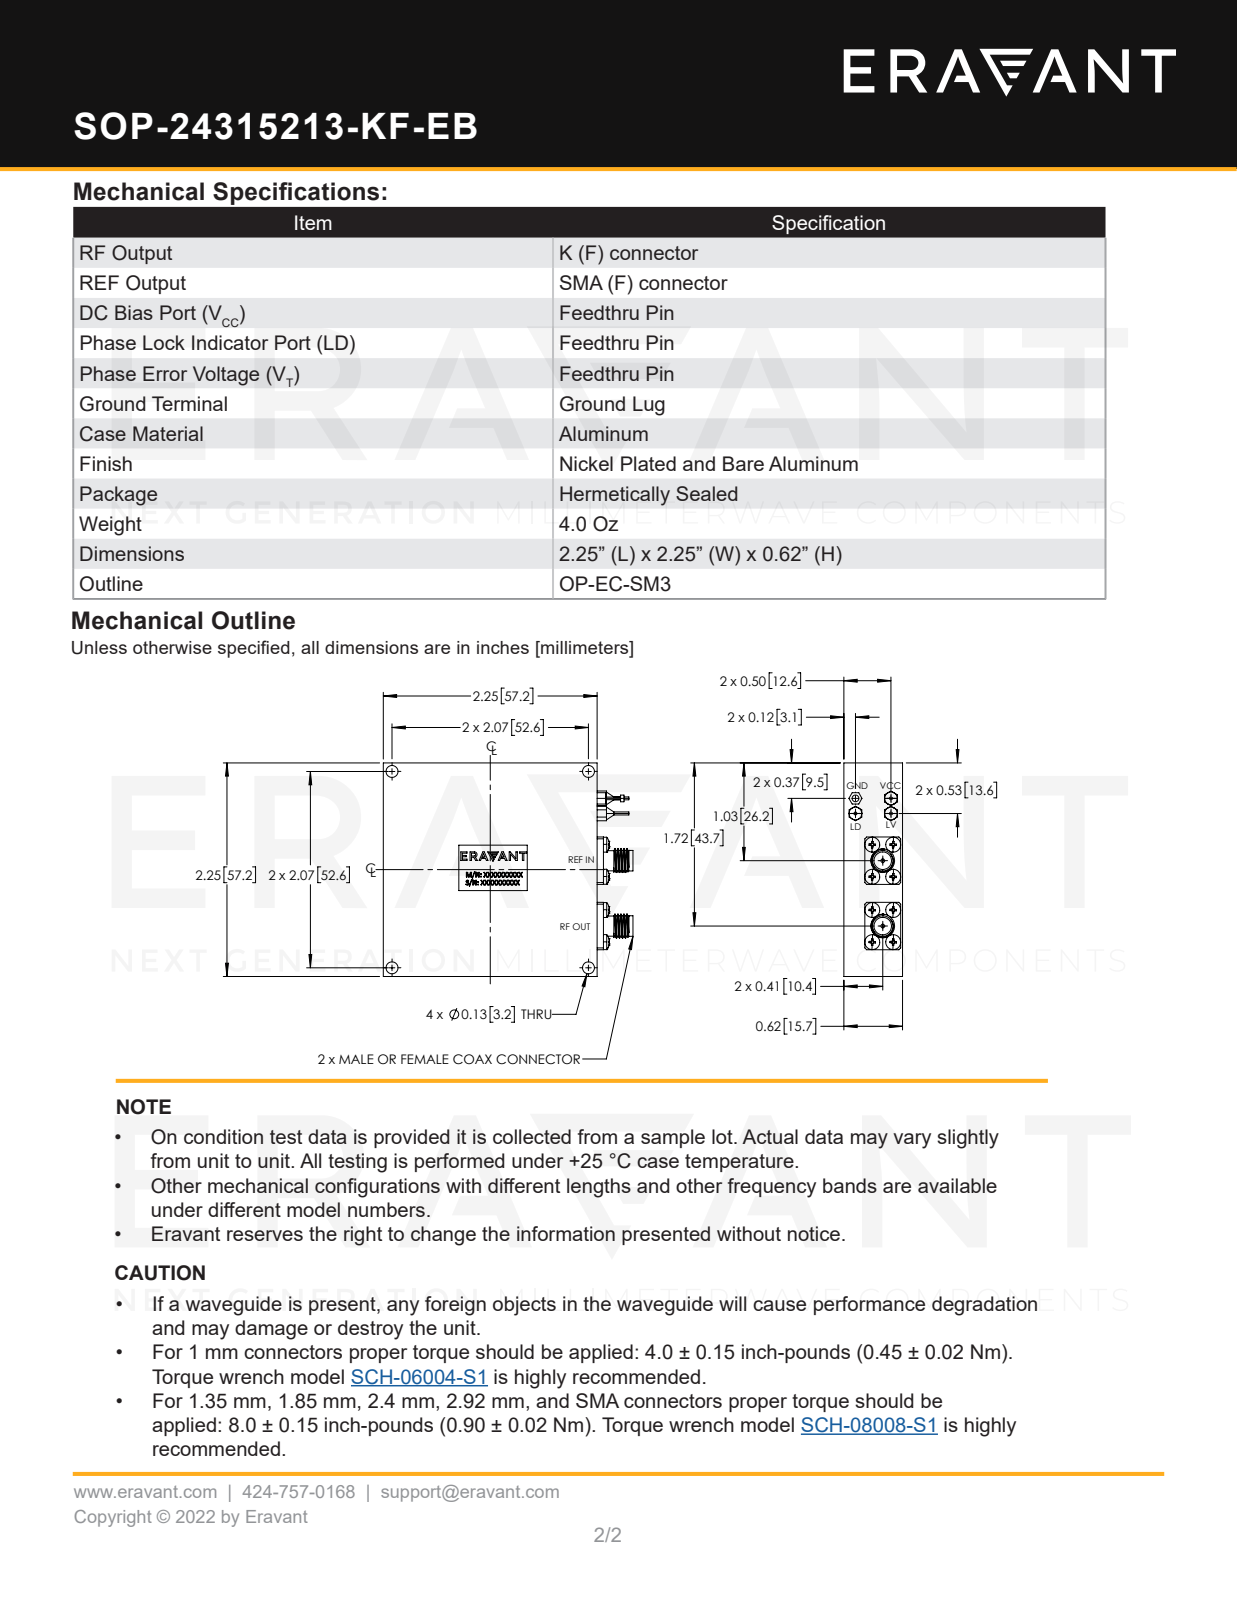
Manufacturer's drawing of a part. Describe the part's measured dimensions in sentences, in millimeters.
The part is named "SOP-09301113-SF-EB". Its 3-D file was written by "SolidWorks 2021 (AUTOMOTIVE_DESIGN)". It is 1 solid with 375 faces: 199 planar, 136 cylindrical and 40 other. Overall it measures 66.8 by 57.2 by 15.7 millimeters. Its volume is 51 801 cubic millimeters and its surface area 11 893 square millimeters. Round holes: 8 of diameter 2.7, 4 of diameter 3.2, 3 of diameter 1, 2 of diameter 4.7. Round bosses or shafts: 8 of diameter 4, 8 of diameter 2, 3 of diameter 0.8, 2 of diameter 6.35, 2 of diameter 5.5, 2 of diameter 5.4, 1 of diameter 1.8, 1 of diameter 0.7. Partial cylindrical surfaces (rounded edges, fillets, slot ends): 32 of radius 0.3. The main face-to-face distances are 15.7, 57.2, 1.7, 58.9, 9.6, 3.4, 5.6, 10.1, 15.2, 0.5. The hole center spacings are 5.13, 17.5, 5.6, 8.6, 10.26, 13.49, 18.37, 21.98.
